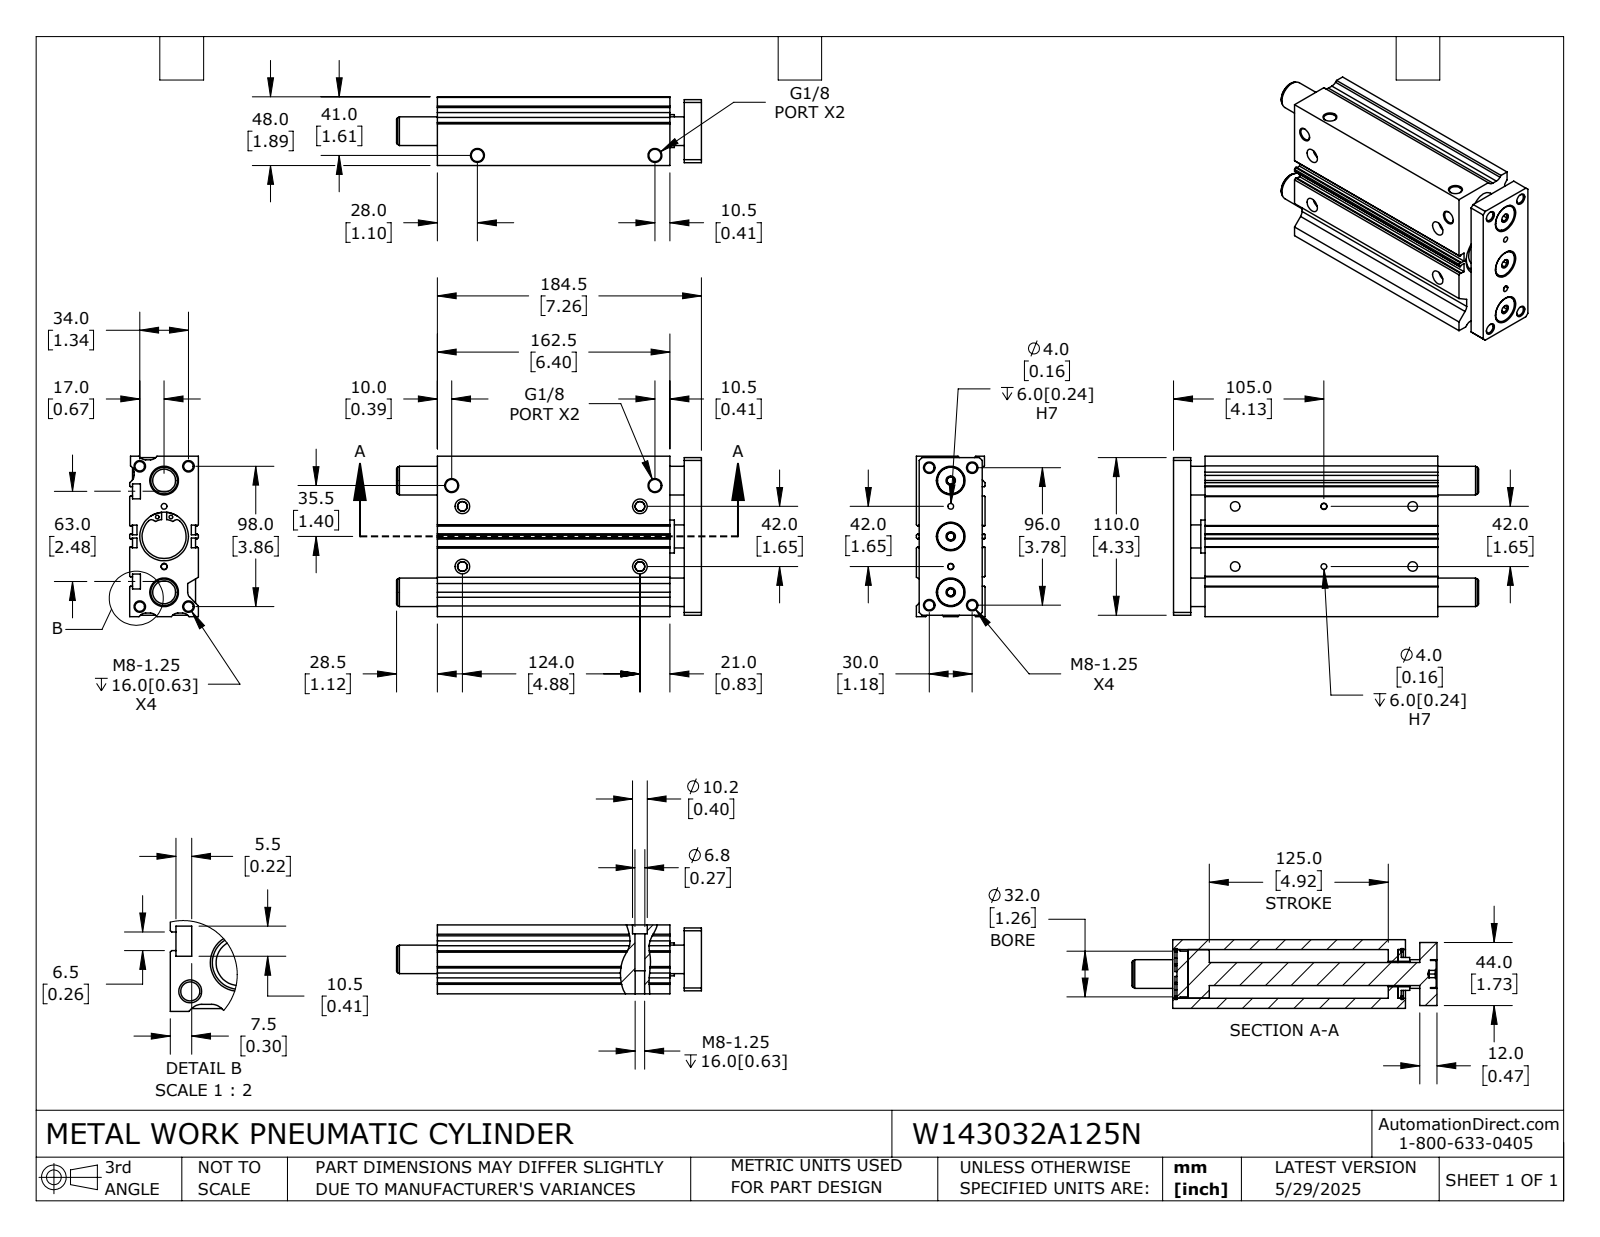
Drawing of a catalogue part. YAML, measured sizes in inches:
part_name: "W143032A125N_ROD; W143032A125N; W143032A125N_BODY"
step_written_by: "SolidWorks 2024 (CONFIG_CONTROL_DESIGN)"
units: inches
bodies: {solids: 6, faces: 394, planar: 195, cylindrical: 149, other: 50}
overall_size: [8.386, 4.409, 1.89]
volume: 47.13
surface_area: 278.3
round_holes:
  - {diameter: 0.262, count: 12}
  - {diameter: 0.098, count: 4}
  - {diameter: 0.157, count: 4}
  - {diameter: 0.268, count: 4}
  - {diameter: 0.337, count: 4}
  - {diameter: 0.402, count: 4}
  - {diameter: 0.197, count: 3}
  - {diameter: 0.787, count: 3}
  - {diameter: 0.697, count: 1}
  - {diameter: 1.211, count: 1}
round_bosses_or_shafts:
  - {diameter: 0.748, count: 3}
  - {diameter: 1.406, count: 2}
  - {diameter: 1.339, count: 1}
  - {diameter: 1.26, count: 1}
  - {diameter: 0.906, count: 1}
  - {diameter: 0.63, count: 1}
partial_cylinders:
  - {radius: 0.197, count: 9}
  - {radius: 0.079, count: 4}
  - {radius: 0.118, count: 4}
  - {radius: 0.507, count: 2}
face_to_face_distances: [1.89, 0.118, 0.295, 0.098, 1.693, 0.079, 0.197, 1.594, 0.472, 0.866]
hole_center_spacings: [0.088, 0.348, 0.566, 0.689, 0.776, 1.019, 1.216, 1.261]
